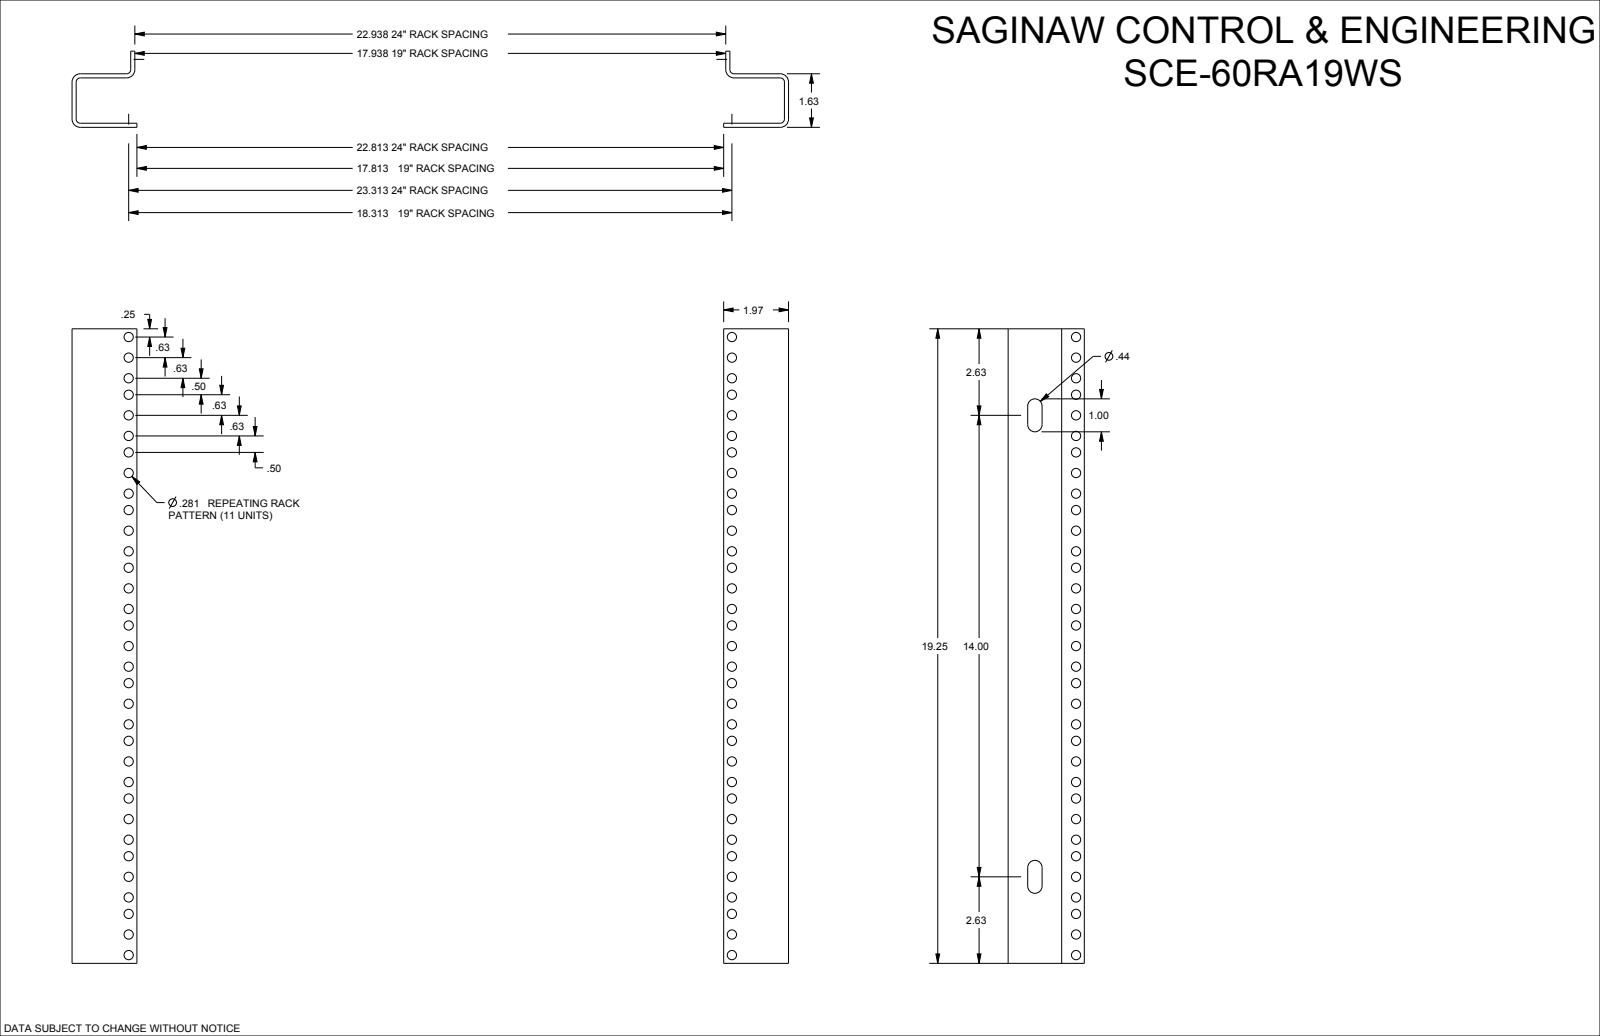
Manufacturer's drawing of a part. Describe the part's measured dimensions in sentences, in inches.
The part is named "SCE-60RA19WS". Its 3-D file was written by "SolidWorks 2019 (CONFIG_CONTROL_DESIGN)". It is 2 solids with 184 faces: 32 planar, 152 cylindrical and 0 other. Overall it measures 21.751 by 19.25 by 2.312 inches. Its volume is 26.19 cubic inches and its surface area 447.3 square inches. Round holes: 103 of diameter 0.281. Partial cylindrical surfaces (rounded edges, fillets, slot ends): 6 of radius 0.125, 6 of radius 0.25, 4 of radius 0.219. The main face-to-face distances are 0.125, 0.125, 1.5, 1.625, 1.375, 1.5, 19.844, 21.75, 21.626, 21.625. The hole center spacings are 1.75, 3.5, 5.25, 7, 8.75, 10.5, 0.625, 0.625.
